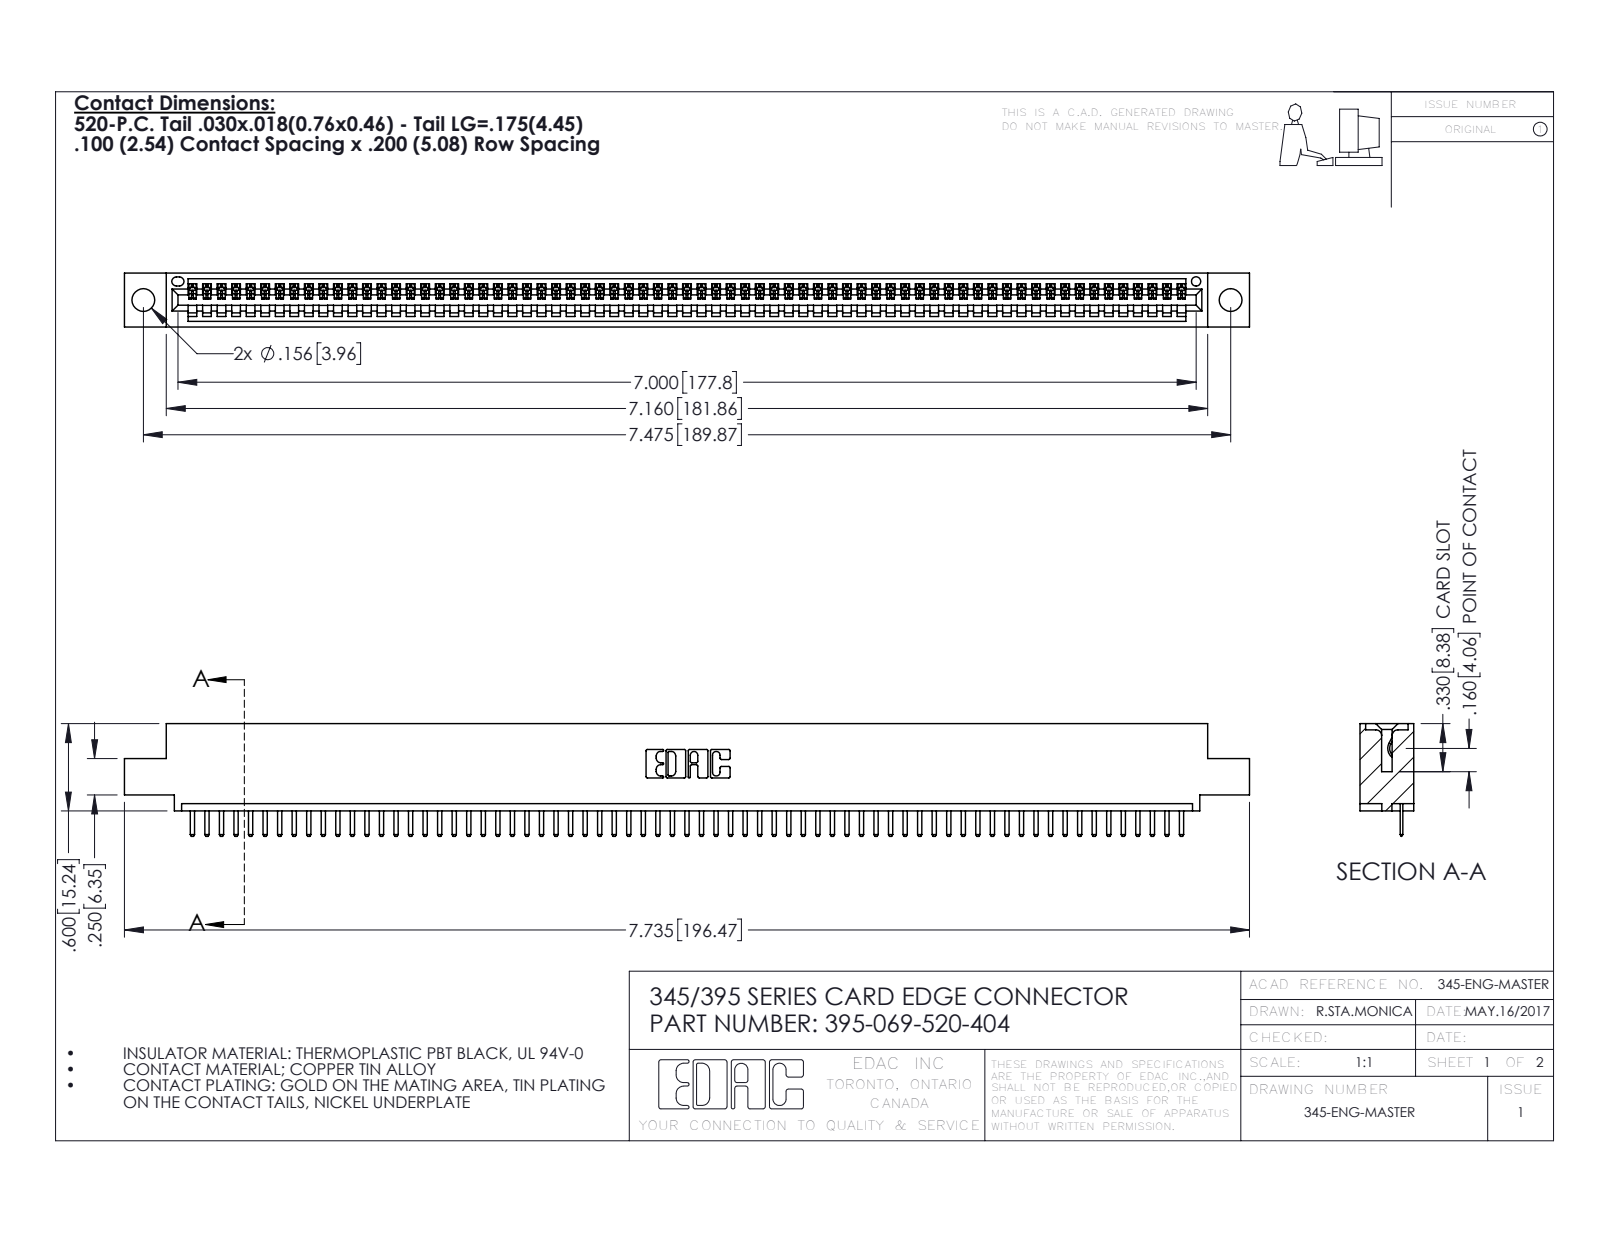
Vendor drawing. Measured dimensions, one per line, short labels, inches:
name: 395-069-520-404; 345 Part_0.110 Offset - 0.156 Dia-TH; 345-292-001_345-293-120
written by: SolidWorks 2016 (CONFIG_CONTROL_DESIGN)
unit: in
bodies: 70 solids, 4408 faces (2982 planar, 1426 cylindrical, 0 other)
size: 7.735 × 0.775 × 0.37
volume: 1.13 in³; area: 37.55 in²
holes: 2× ⌀0.156, 1× ⌀0.064
rounds: 140× R0.01, 138× R0.006, 22× R0.01, 6× R0.007, 6× R0.031, 3× R0.026, 2× R0.031, 2× R0.04
face distances: 0.072, 0.298, 0.37, 0.2, 0.098, 0.272, 0.025, 0.225, 0.072, 0.149
hole spacings: 0.27, 7.239, 7.475
